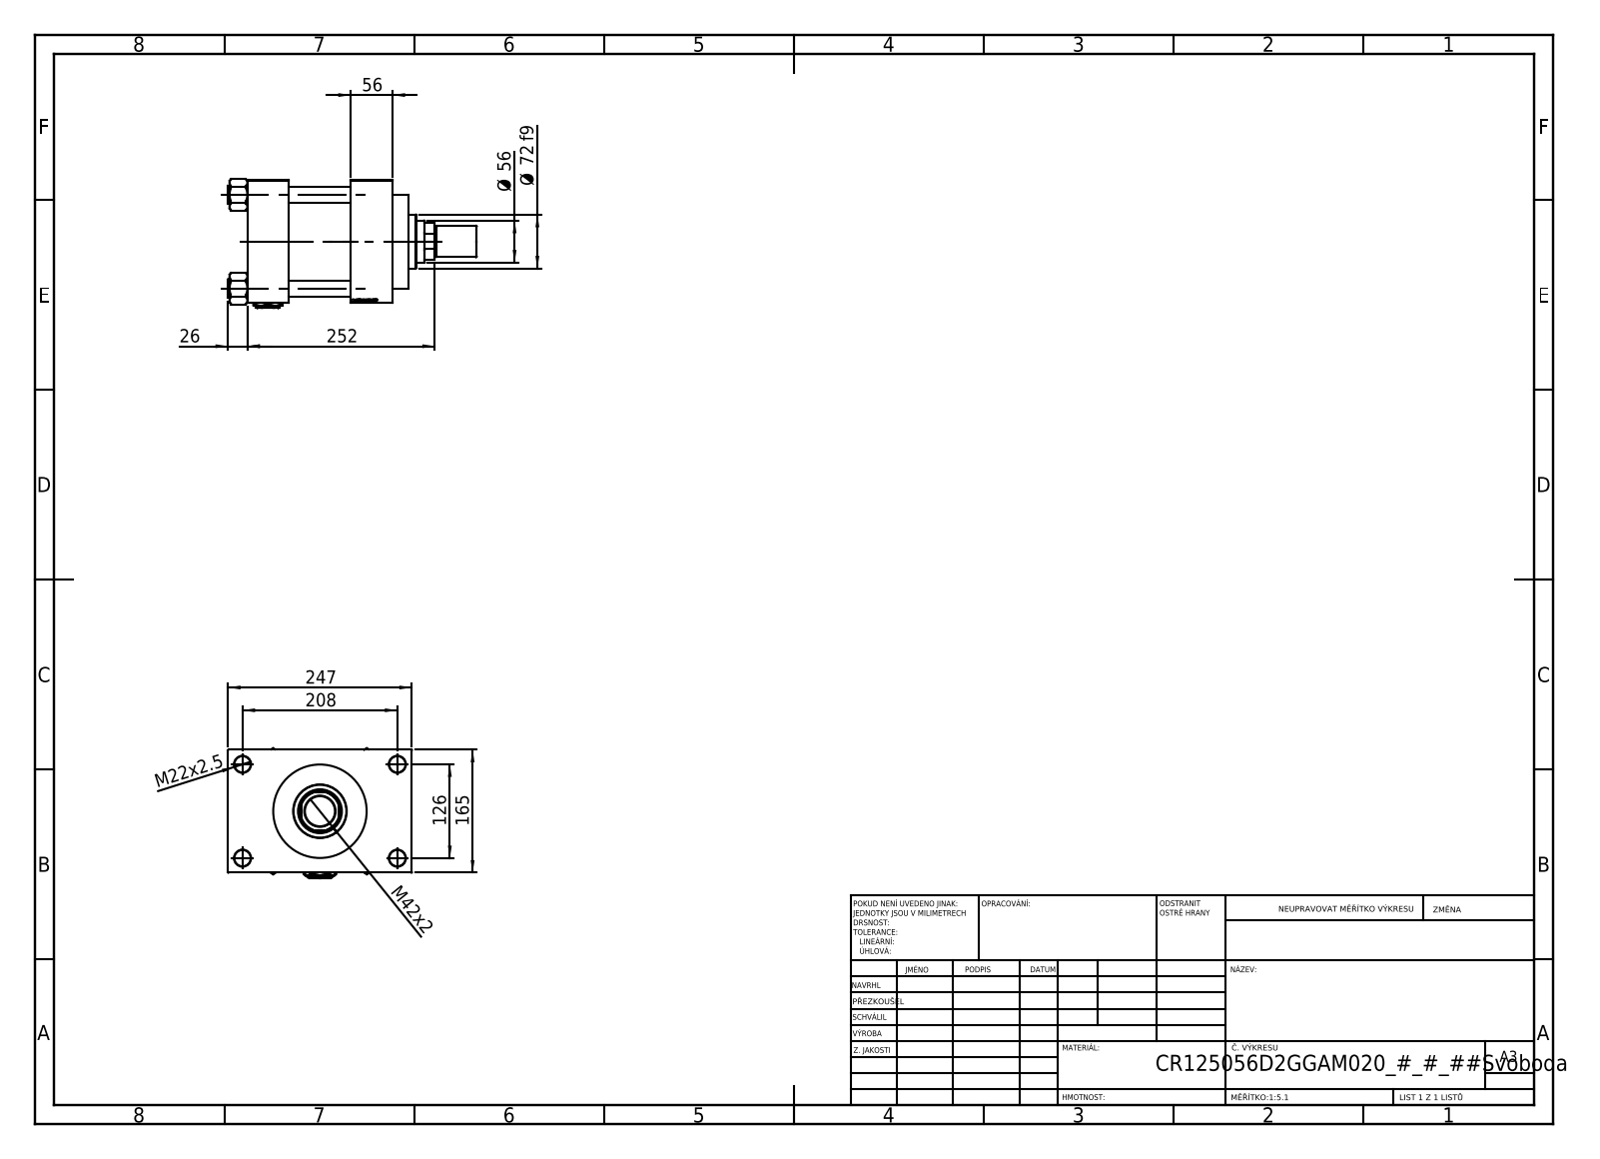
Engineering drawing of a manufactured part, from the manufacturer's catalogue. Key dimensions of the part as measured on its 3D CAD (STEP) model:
Part name (STEP PRODUCT): V215_VC_A; V215CR_VCP_D; ROD_END_AH; V215CR_D_TYCINKA (+3 more)
STEP written by: SolidWorks 2019 (CONFIG_CONTROL_DESIGN)
Units: millimetres
Bodies: 13 solids, 1216 faces (572 planar, 98 cylindrical, 546 other)
Overall size (bounding box): 334 × 247 × 174.07
Volume: 5 031 000 mm³ · Surface area: 546 062 mm²
Round holes (diameter × count): ⌀22 ×8, ⌀7 ×2, ⌀32.24 ×2, ⌀45 ×2, ⌀40.5 ×1, ⌀56 ×1, ⌀59 ×1, ⌀96 ×1, ⌀125 ×1, ⌀125.5 ×1
Round bosses / shafts (diameter × count): ⌀25 ×4, ⌀131 ×1, ⌀72 ×1, ⌀42 ×1, ⌀40 ×1
Partial cylindrical surfaces — rounded edges, fillets, slot ends (radius × count): R27 ×1
Main face-to-face distances: 165, 84, 55, 139, 56, 195, 140, 41, 206, 173.74
Hole centre spacings: 41.05, 89.02, 121.59, 125.9, 132.47, 166.95, 209.13, 126
